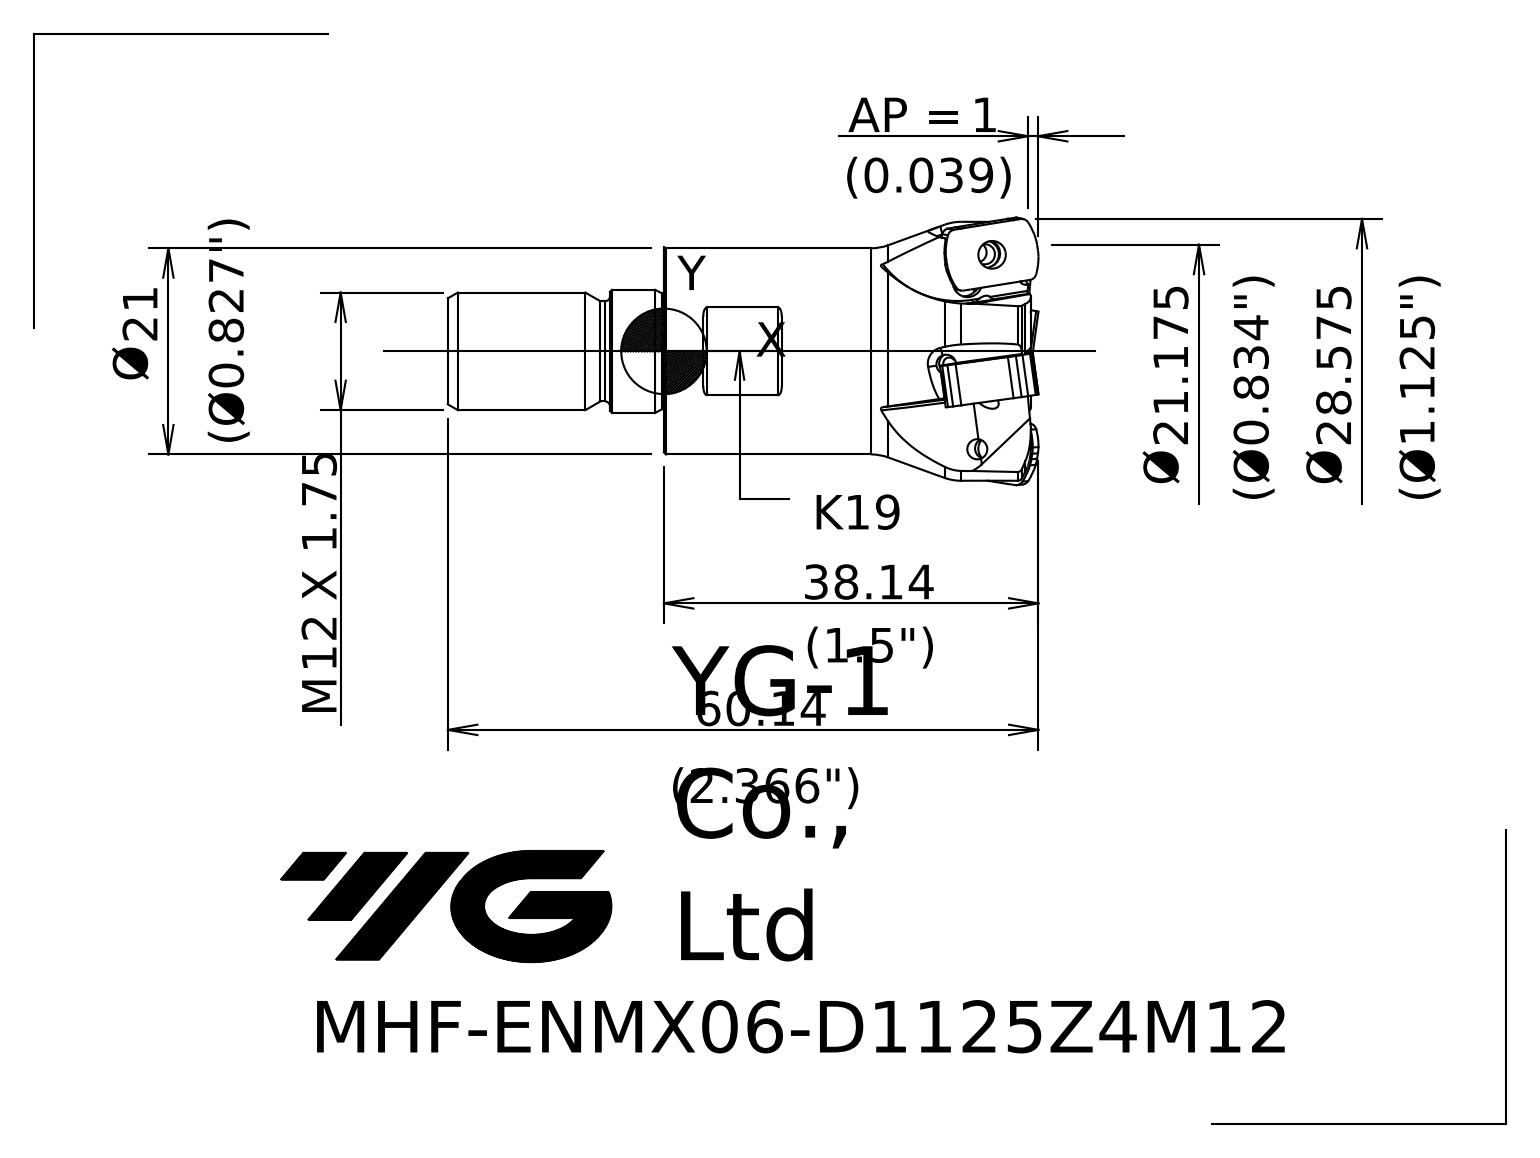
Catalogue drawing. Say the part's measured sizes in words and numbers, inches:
The part is named "120116A4801F3c9i". Its 3-D file was written by "SIEMENS PLM Software NX 10.0 (AP203_CONFIGURATION_CONTROLLED_3D_DESIGN_OF_MECHANICAL_PARTS_AND_ASSEMBLIES_MIM_LF)". It is 1 solid with 74 faces: 13 planar, 11 cylindrical and 50 other. Overall it measures 2.366 by 1.126 by 1.126 inches. Its volume is 1.013 cubic inches and its surface area 8.762 square inches. Round holes: 1 of diameter 0.059, 1 of diameter 0.236. Round bosses or shafts: 1 of diameter 0.827, 1 of diameter 0.492, 1 of diameter 0.471, 1 of diameter 0.425, 1 of diameter 0.387. Partial cylindrical surfaces (rounded edges, fillets, slot ends): 4 of radius 0.016. The main face-to-face distances are 1.453, 0.748, 2.319, 0.866, 0.374, 1.669, 0.217, 0.65, 1.295, 0.157.
